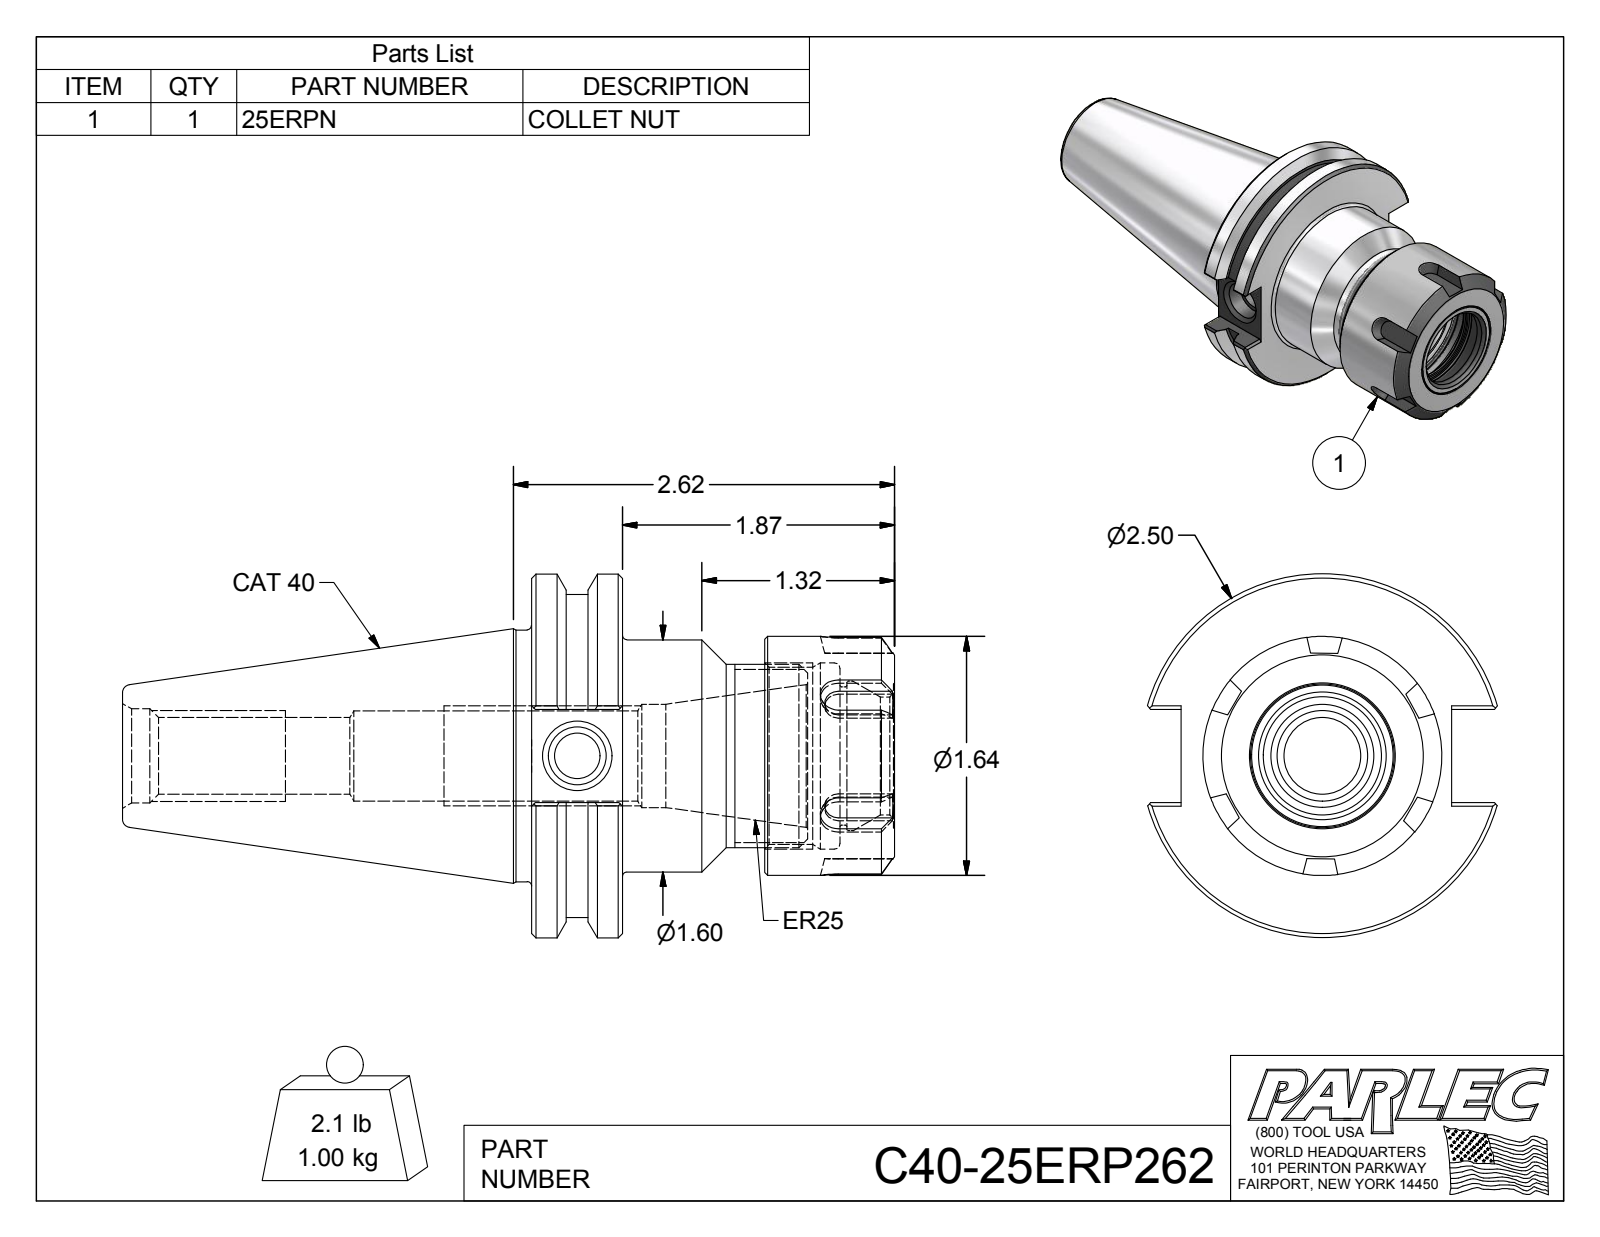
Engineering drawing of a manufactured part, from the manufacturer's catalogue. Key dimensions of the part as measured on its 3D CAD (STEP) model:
Part name (STEP PRODUCT): C40-25ERP262; C40-25ER2-1; 25ERPN
STEP written by: Autodesk Inventor 2012 (AUTOMOTIVE_DESIGN)
Units: inches
Bodies: 2 solids, 117 faces (54 planar, 21 cylindrical, 42 other)
Overall size (bounding box): 5.308 × 2.5 × 2.403
Volume: 8.294 in³ · Surface area: 50.62 in²
Round holes (diameter × count): ⌀0.315 ×1, ⌀0.396 ×1, ⌀0.527 ×1, ⌀0.62 ×1, ⌀0.648 ×1, ⌀0.71 ×1, ⌀0.811 ×1, ⌀0.95 ×1, ⌀1.027 ×1, ⌀1.217 ×1, ⌀1.28 ×1
Round bosses / shafts (diameter × count): ⌀2.5 ×1, ⌀2.219 ×1, ⌀1.73 ×1, ⌀1.643 ×1, ⌀1.595 ×1, ⌀1.26 ×1
Main face-to-face distances: 0.625, 2.495, 1.87, 1.602, 0.977, 0.893, 2.12, 1.495, 0.518, 0.375
